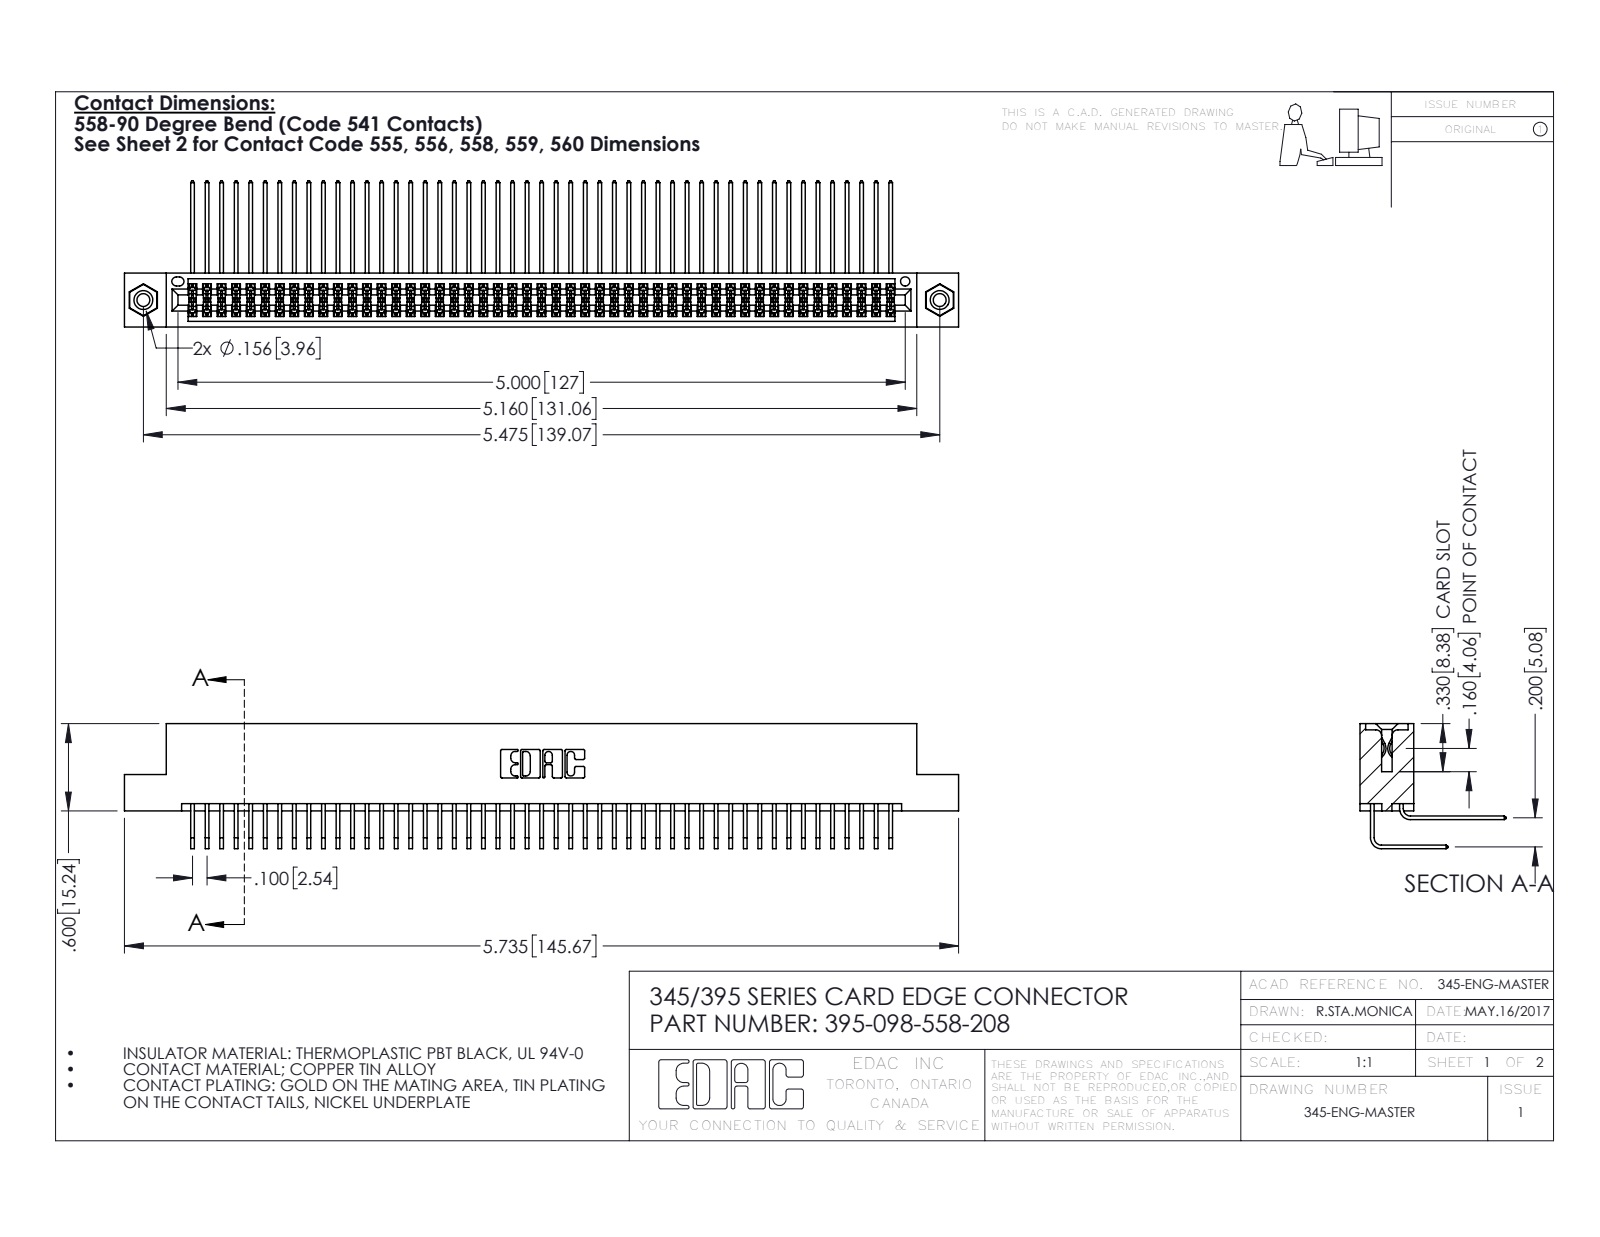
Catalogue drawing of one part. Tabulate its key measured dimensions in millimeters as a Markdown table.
| quantity | value |
| --- | --- |
| part name | 345-250-001_345-250-003-102; 345-292-001_558 Tail - 2; 345-292-001_558 559 Tail - 1; 345 Part_Flush Mounting Lugs - 0.156 Dia-TI (+1 more) |
| STEP written by | SolidWorks 2016 (CONFIG_CONTROL_DESIGN) |
| units | millimeters |
| bodies | 101 solids, 5282 faces (3542 planar, 1724 cylindrical, 16 other) |
| overall size | 145.7 × 25.5 × 21.8 |
| volume | 14 800 mm³ |
| surface area | 24 650 mm² |
| round holes (diameter × count) | 2.3 × 2, 3.2 × 2, 4 × 2, 1.6 × 1 |
| round bosses / shafts (diameter × count) | 3.9 × 2 |
| partial cylindrical surfaces (radius × count) | 0.2 × 148, 0.3 × 22, 0.2 × 6, 0.8 × 6, 0.7 × 3, 0.4 × 2, 0.5 × 2, 0.6 × 2 |
| main face-to-face distances | 1.8, 7.6, 5.1, 9.4, 2.5, 6.9, 0.6, 5.7, 0.6, 4.4 |
| hole center spacings | 6.9, 133.1, 139.1 |
